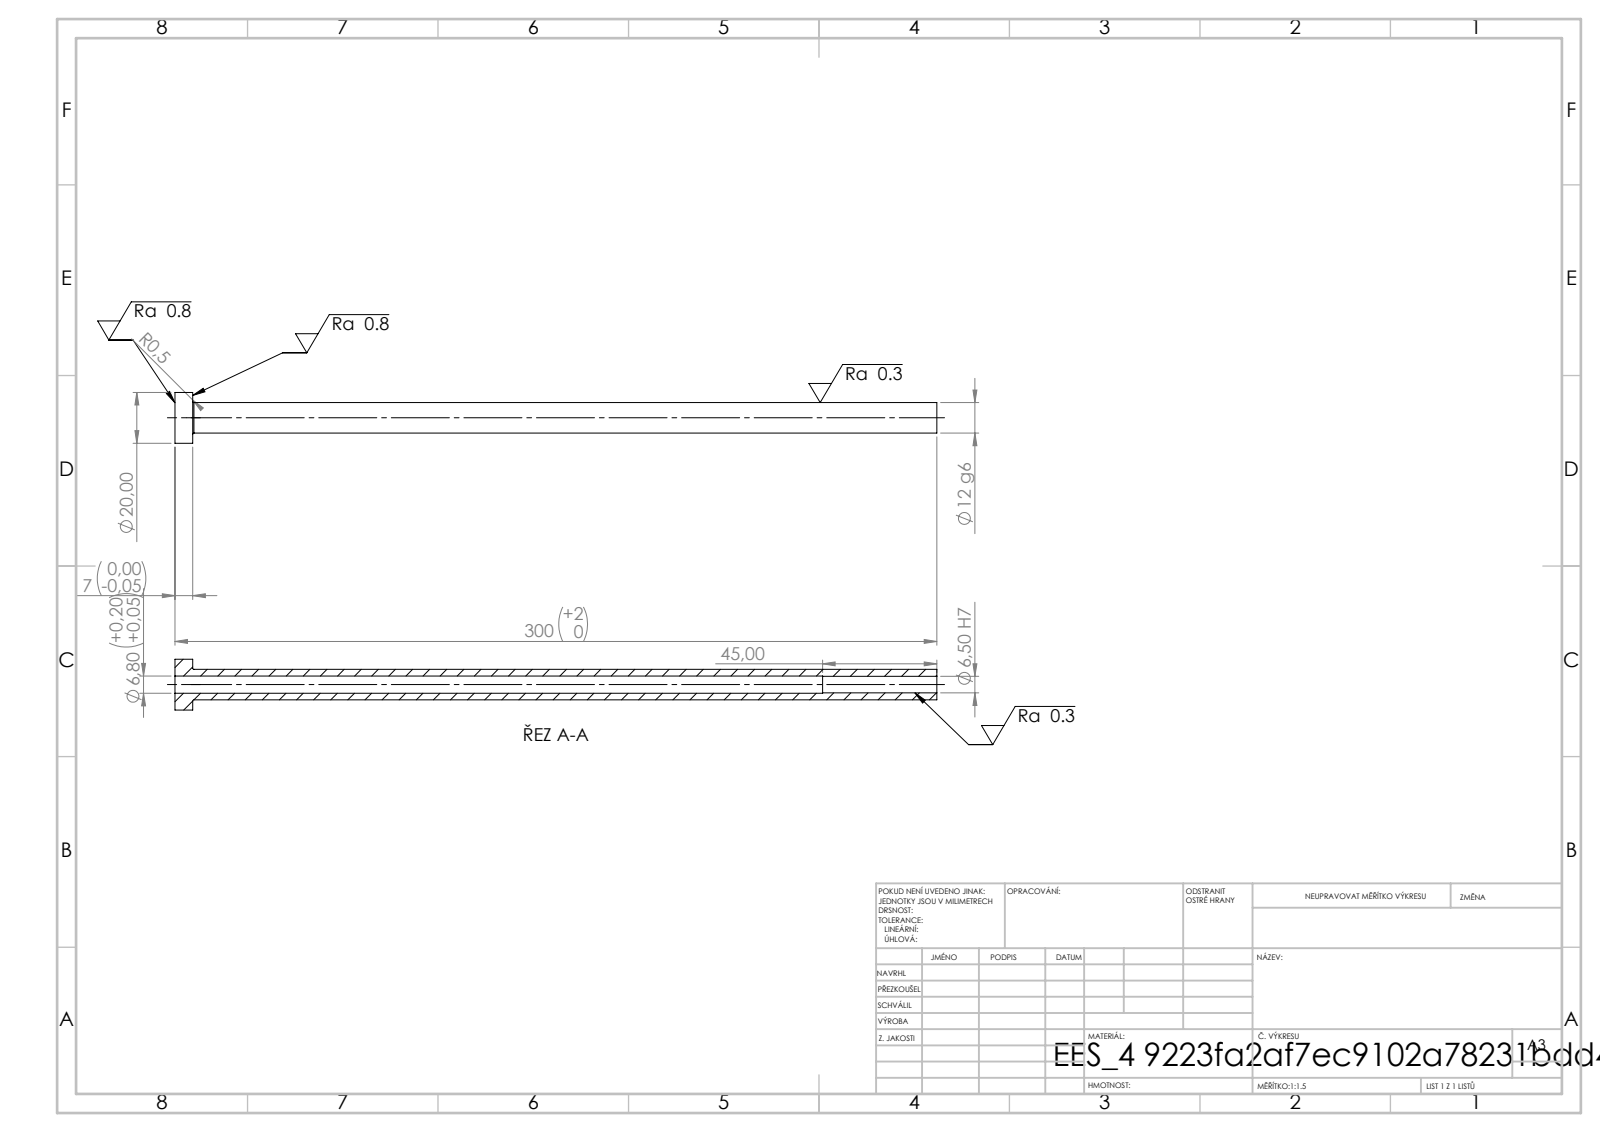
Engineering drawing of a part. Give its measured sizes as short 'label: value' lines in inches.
written by: SolidWorks 2019 (CONFIG_CONTROL_DESIGN)
unit: in
bodies: 1 solid, 14 faces (4 planar, 8 cylindrical, 2 other)
size: 11.811 × 0.787 × 0.787
volume: 1.5 in³; area: 28.53 in²
holes: 1× ⌀0.256, 1× ⌀0.268
bosses: 1× ⌀0.787, 1× ⌀0.472
face distances: 0.276, 11.811, 11.535, 10.039, 9.764, 1.772
